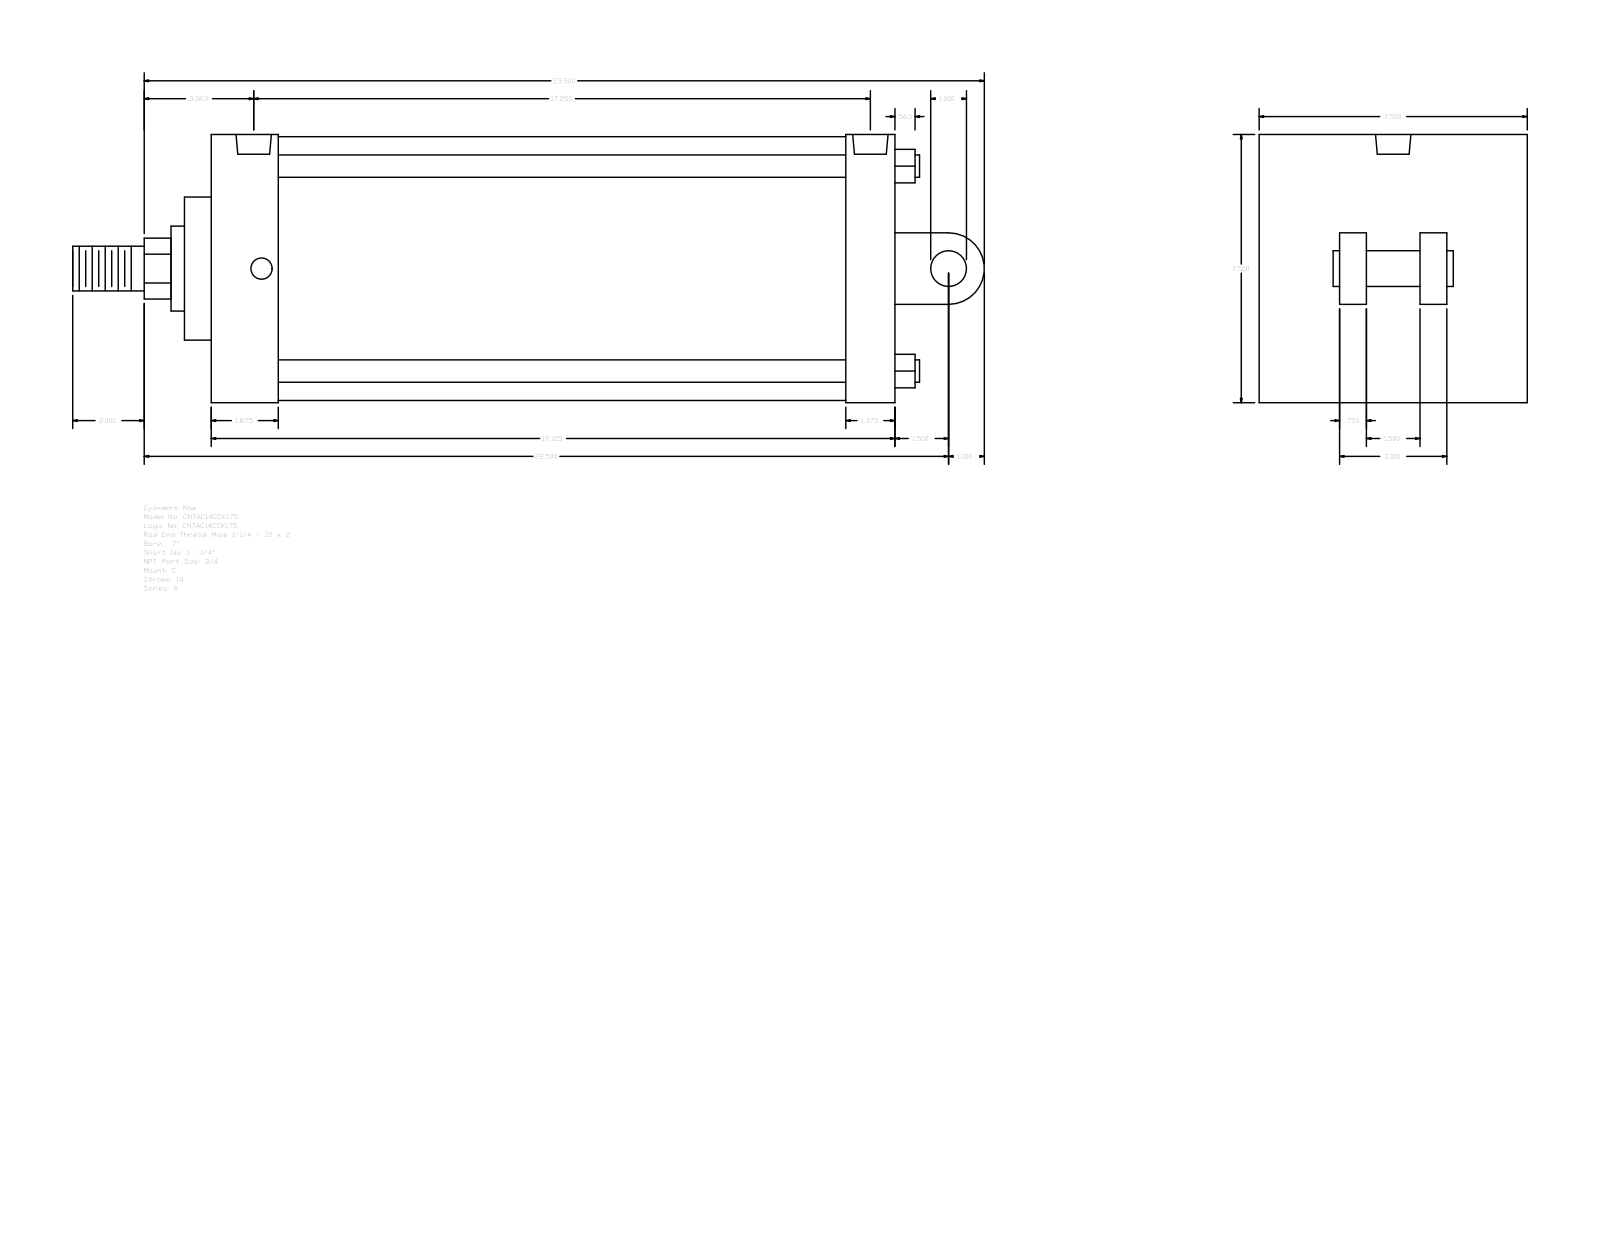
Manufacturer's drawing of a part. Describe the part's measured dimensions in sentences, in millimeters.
The part is named "A_C__0700_1.75". Its 3-D file was written by "GSSL Pune (CONFIG_CONTROL_DESIGN)". It is 0 solids with 104 faces: 75 planar, 29 cylindrical and 0 other. Overall it measures 647.7 by 190.5 by 190.5 millimeters. Round holes: 4 of diameter 15.08, 2 of diameter 25.12. Round bosses or shafts: 4 of diameter 15.88, 1 of diameter 187.32, 1 of diameter 60.33, 1 of diameter 44.45, 1 of diameter 31.75, 1 of diameter 25.4. Partial cylindrical surfaces (rounded edges, fillets, slot ends): 1 of radius 21.63, 1 of radius 25.4. The main face-to-face distances are 190.5, 485.78, 19.05, 76.2, 57.15, 146.05, 44.45, 69.85, 47.63, 438.15. The hole center spacings are 5.56, 427.03, 432.59, 438.15.
